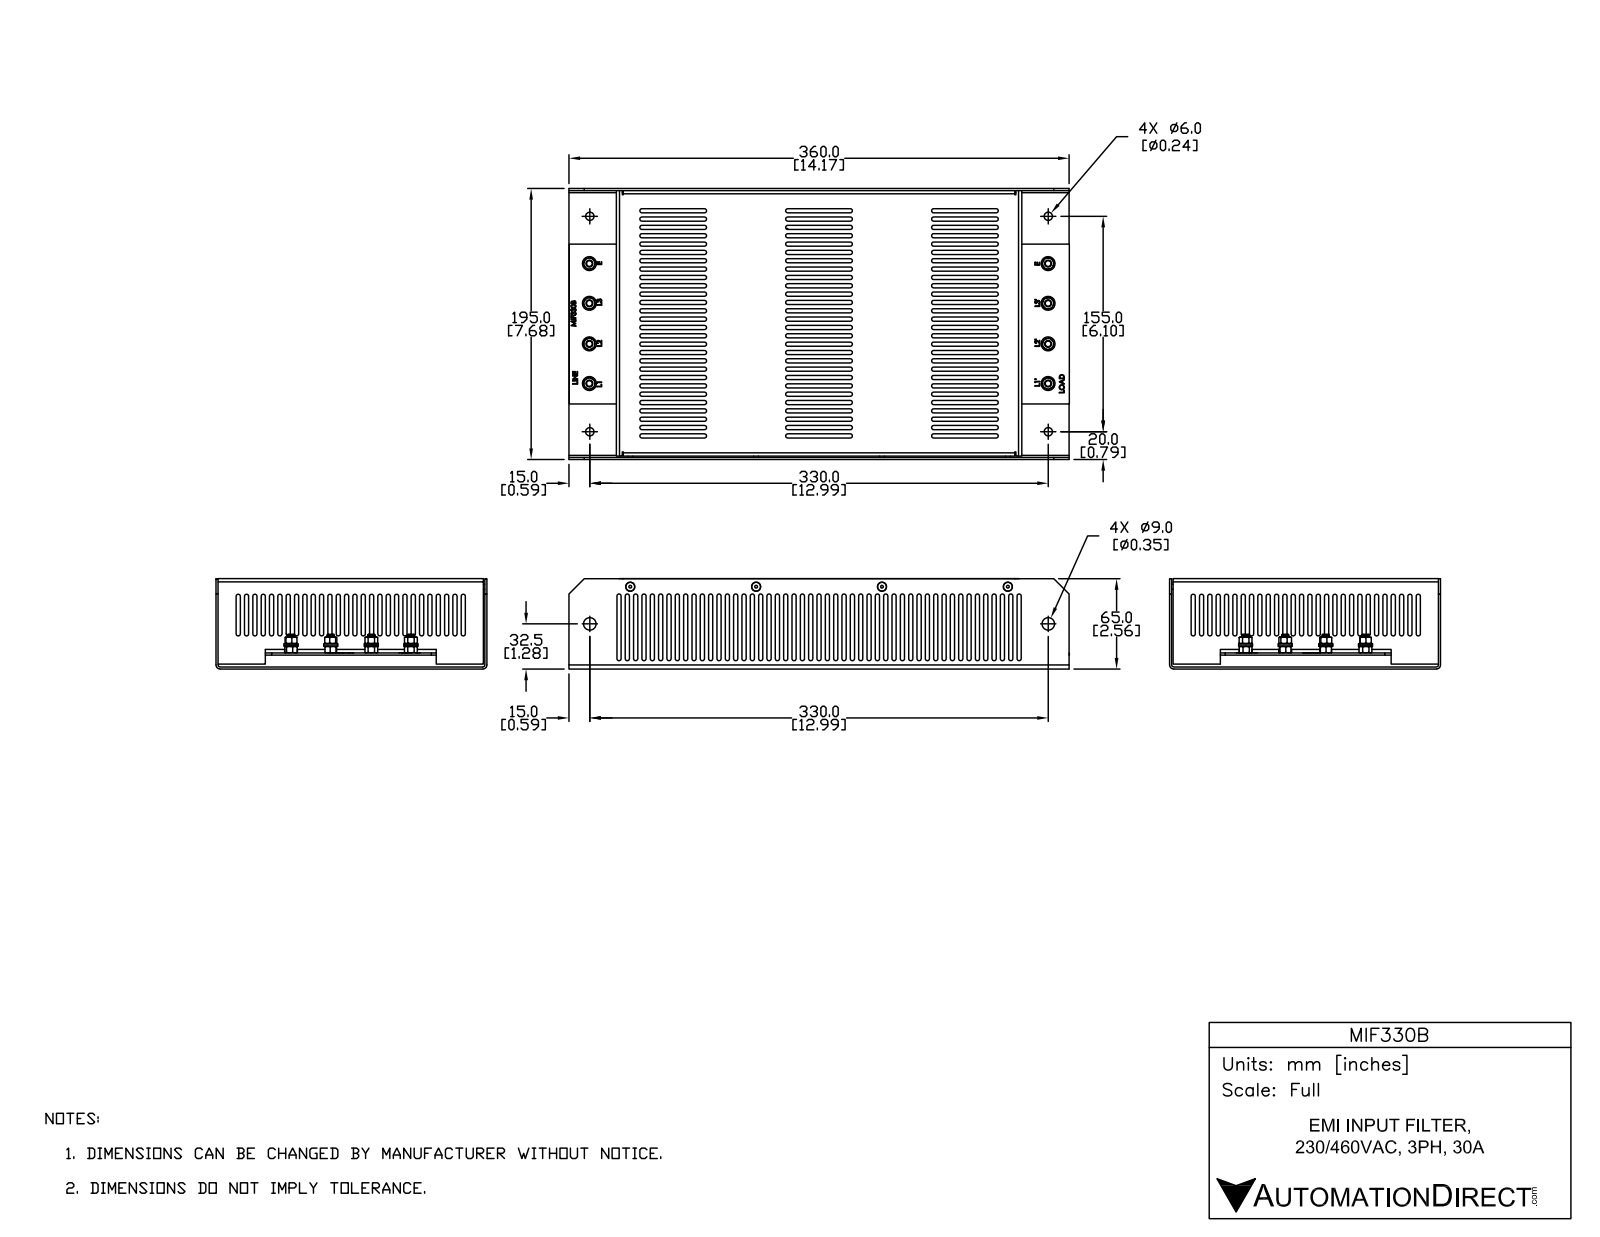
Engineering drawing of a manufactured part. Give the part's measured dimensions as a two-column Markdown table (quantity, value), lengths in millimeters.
| quantity | value |
| --- | --- |
| part name | MIF330B r1 |
| STEP written by | SolidWorks 2017 (AUTOMOTIVE_DESIGN) |
| units | millimeters |
| bodies | 51 solids, 4463 faces (1371 planar, 1604 cylindrical, 1488 other) |
| overall size | 360.2 × 195 × 65 |
| volume | 348 100 mm³ |
| surface area | 499 600 mm² |
| round holes (diameter × count) | 1 × 58, 1.2 × 37, 3.3 × 18, 4 × 18, 4.2 × 8, 5 × 6, 2 × 4, 3.3 × 4, 6 × 4, 9 × 2, 5.1 × 1 |
| round bosses / shafts (diameter × count) | 10 × 8, 5.9 × 8, 5 × 8, 6.4 × 4, 3.5 × 4 |
| partial cylindrical surfaces (radius × count) | 1.5 × 324, 2.7 × 8, 0.8 × 4, 2.3 × 4, 3 × 2 |
| main face-to-face distances | 1.5, 63.6, 10, 8.5, 11.6, 10.1, 1.6, 55, 53.5, 65 |
| hole center spacings | 330.2, 90.6, 15.9, 27.5, 28.5, 28.6, 29.2, 31.8 |
